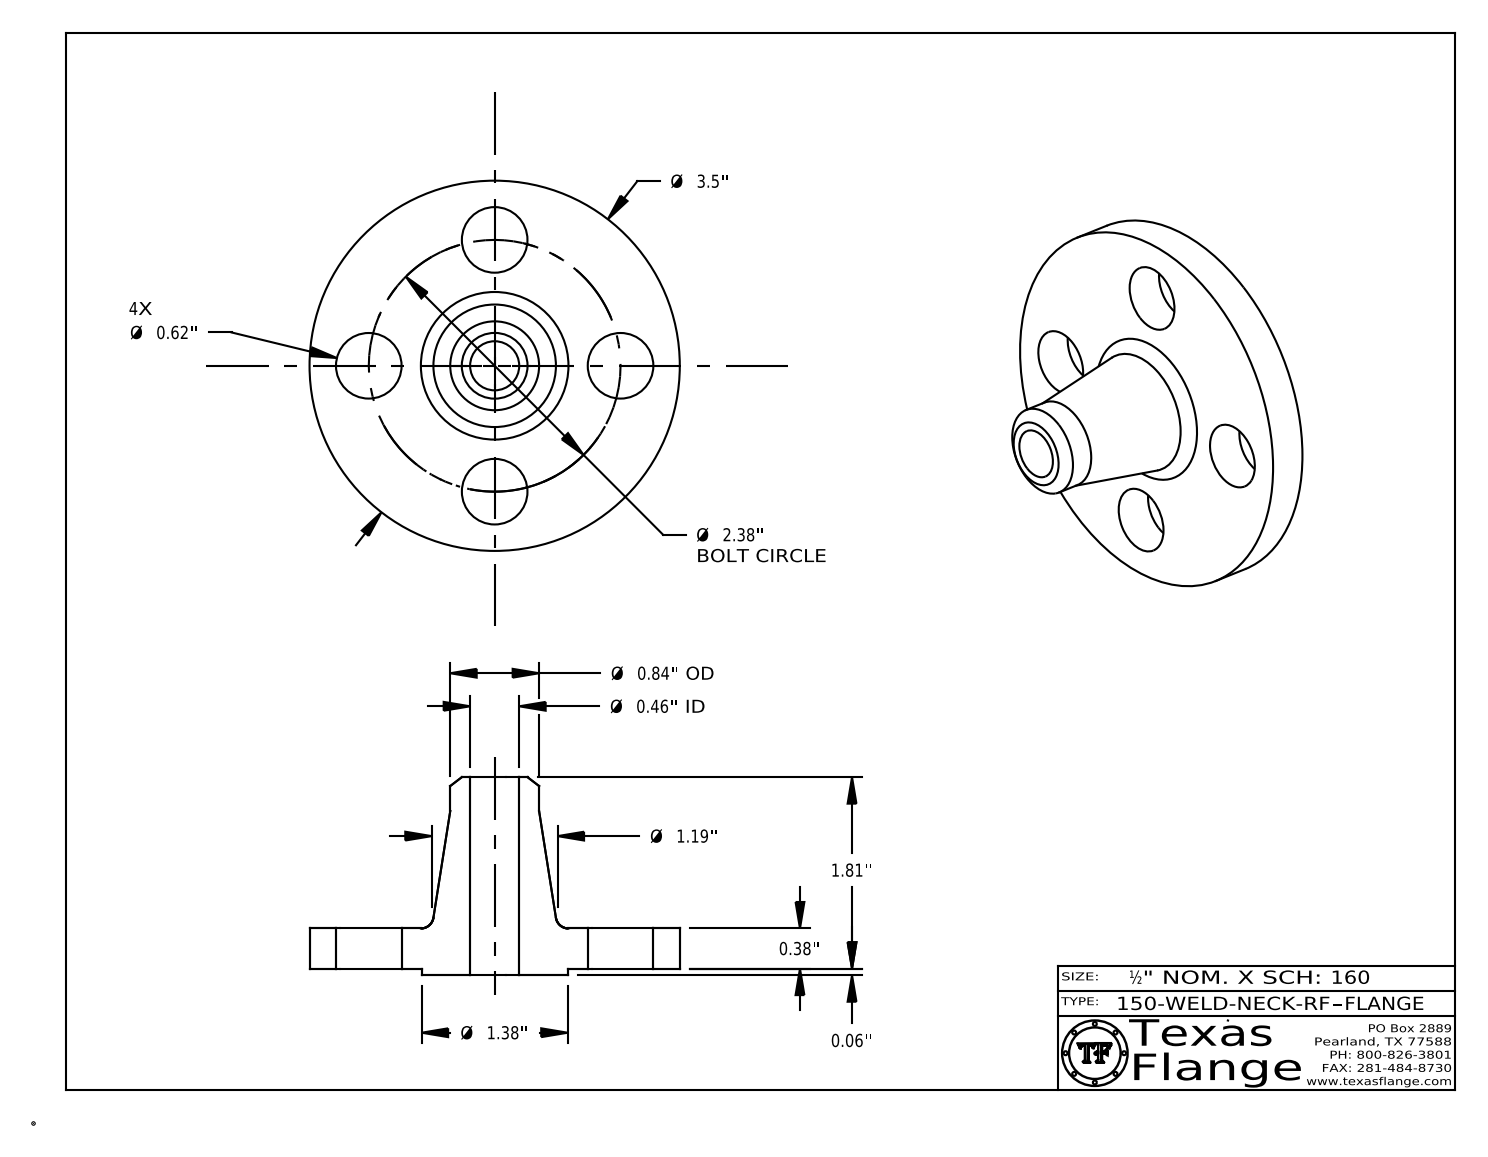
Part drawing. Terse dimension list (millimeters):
name: 150-WELD-NECK-RF
written by: CATIA V5 STEP AP214 (AUTOMOTIVE_DESIGN)
unit: mm
bodies: 1 solid, 411 faces (369 planar, 36 cylindrical, 6 other)
size: 88.9 × 88.9 × 47.6
volume: 66 430 mm³; area: 19 550 mm²
holes: 4× ⌀15.7, 1× ⌀11.8, 1× ⌀12.6
bosses: 8× ⌀0.8, 1× ⌀88.9, 1× ⌀35.1, 1× ⌀21.3, 1× ⌀9.9
face distances: 9.7, 1.6, 11.3, 47.5, 46, 36.3, 10.9, 9.3, 0.4, 36.7
hole spacings: 30.2, 42.7, 23.1, 55.9, 60.5, 30.2
